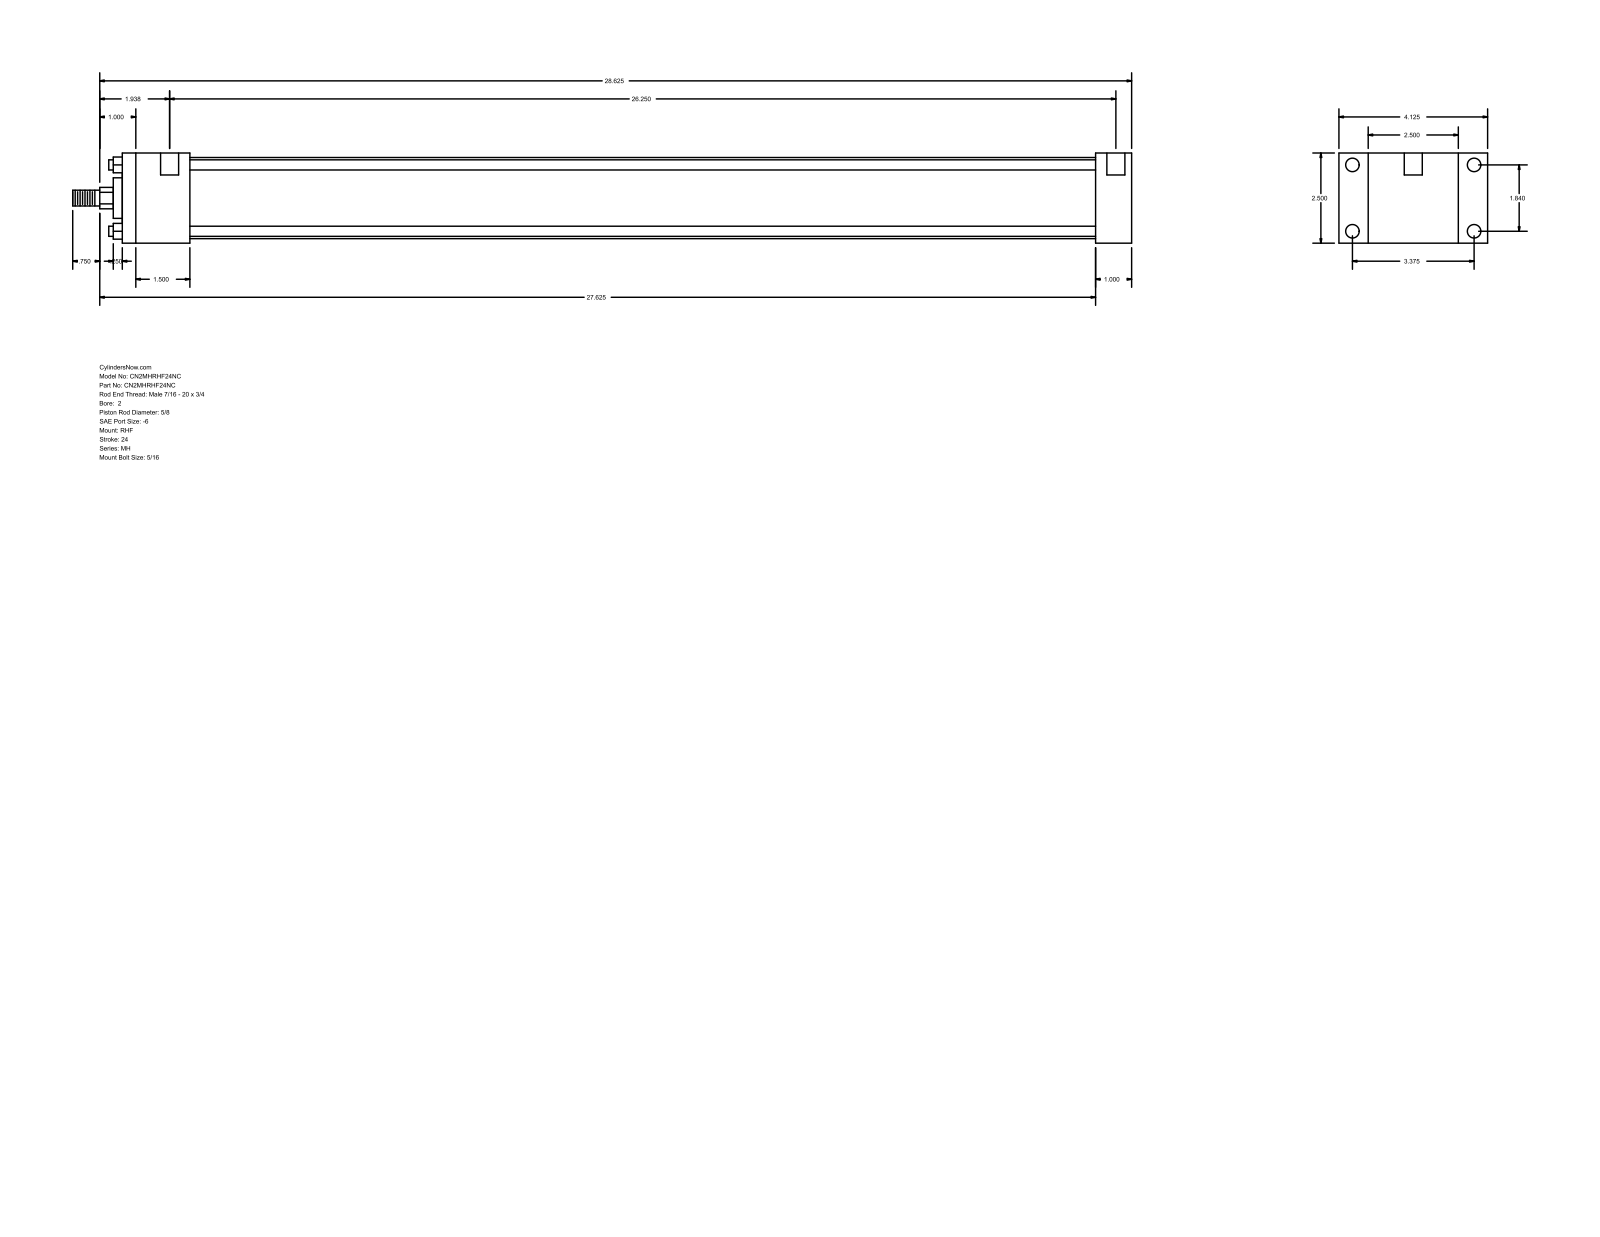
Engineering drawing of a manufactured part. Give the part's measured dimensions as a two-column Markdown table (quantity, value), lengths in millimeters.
| quantity | value |
| --- | --- |
| part name | MH_RHF__0200_0.625 |
| STEP written by | GSSL Pune (CONFIG_CONTROL_DESIGN) |
| units | millimeters |
| bodies | 0 solids, 88 faces (60 planar, 28 cylindrical, 0 other) |
| overall size | 746.12 × 104.78 × 63.5 |
| round holes (diameter × count) | 5.56 × 4, 9.53 × 4, 12.7 × 2 |
| round bosses / shafts (diameter × count) | 7.14 × 4, 57.15 × 1, 28.57 × 1, 15.88 × 1, 11.11 × 1 |
| partial cylindrical surfaces (radius × count) | 7.54 × 1 |
| main face-to-face distances | 63.5, 25.41, 20.64, 84.14, 685.79, 711.2, 104.78, 47.62, 638.17, 663.58 |
| hole center spacings | 46.74, 85.72, 97.63, 674.69, 3.18, 4.76, 666.75, 669.93 |
